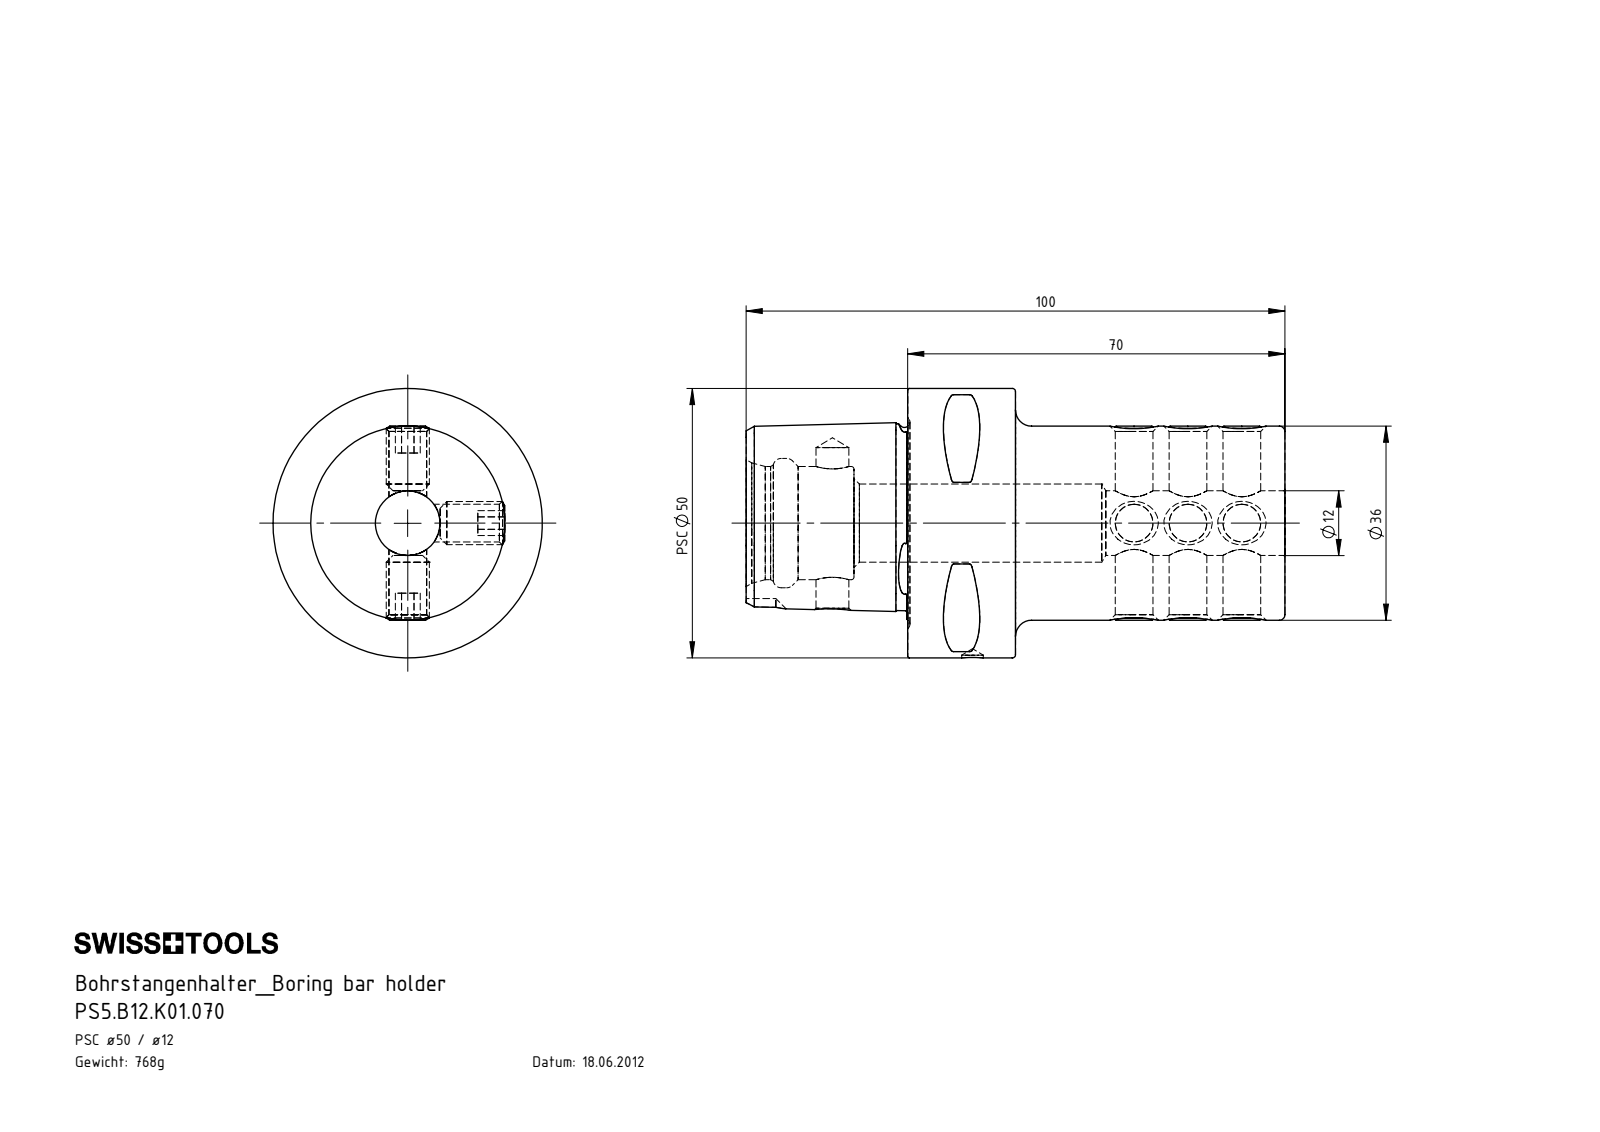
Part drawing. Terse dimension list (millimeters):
name: PS5-B12.K01.070_A; ISO 4026 - M8 x 12_PreviewCfg; PS5.B12.K01.070
written by: SolidWorks 2017 (AUTOMOTIVE_DESIGN)
unit: mm
bodies: 10 solids, 299 faces (101 planar, 65 cylindrical, 133 other)
size: 100 × 50 × 50
volume: 97 802 mm³; area: 26 042 mm²
holes: 6× ⌀7, 1× ⌀4, 1× ⌀6.1, 1× ⌀12, 1× ⌀14.5, 1× ⌀21, 1× ⌀24
bosses: 6× ⌀8, 1× ⌀50, 1× ⌀36
rounds: 8× R0.5, 1× R4
face distances: 50, 70, 20, 30, 10, 5, 100, 4, 12, 24
hole spacings: 10, 20, 26, 30, 40, 50, 56, 66
